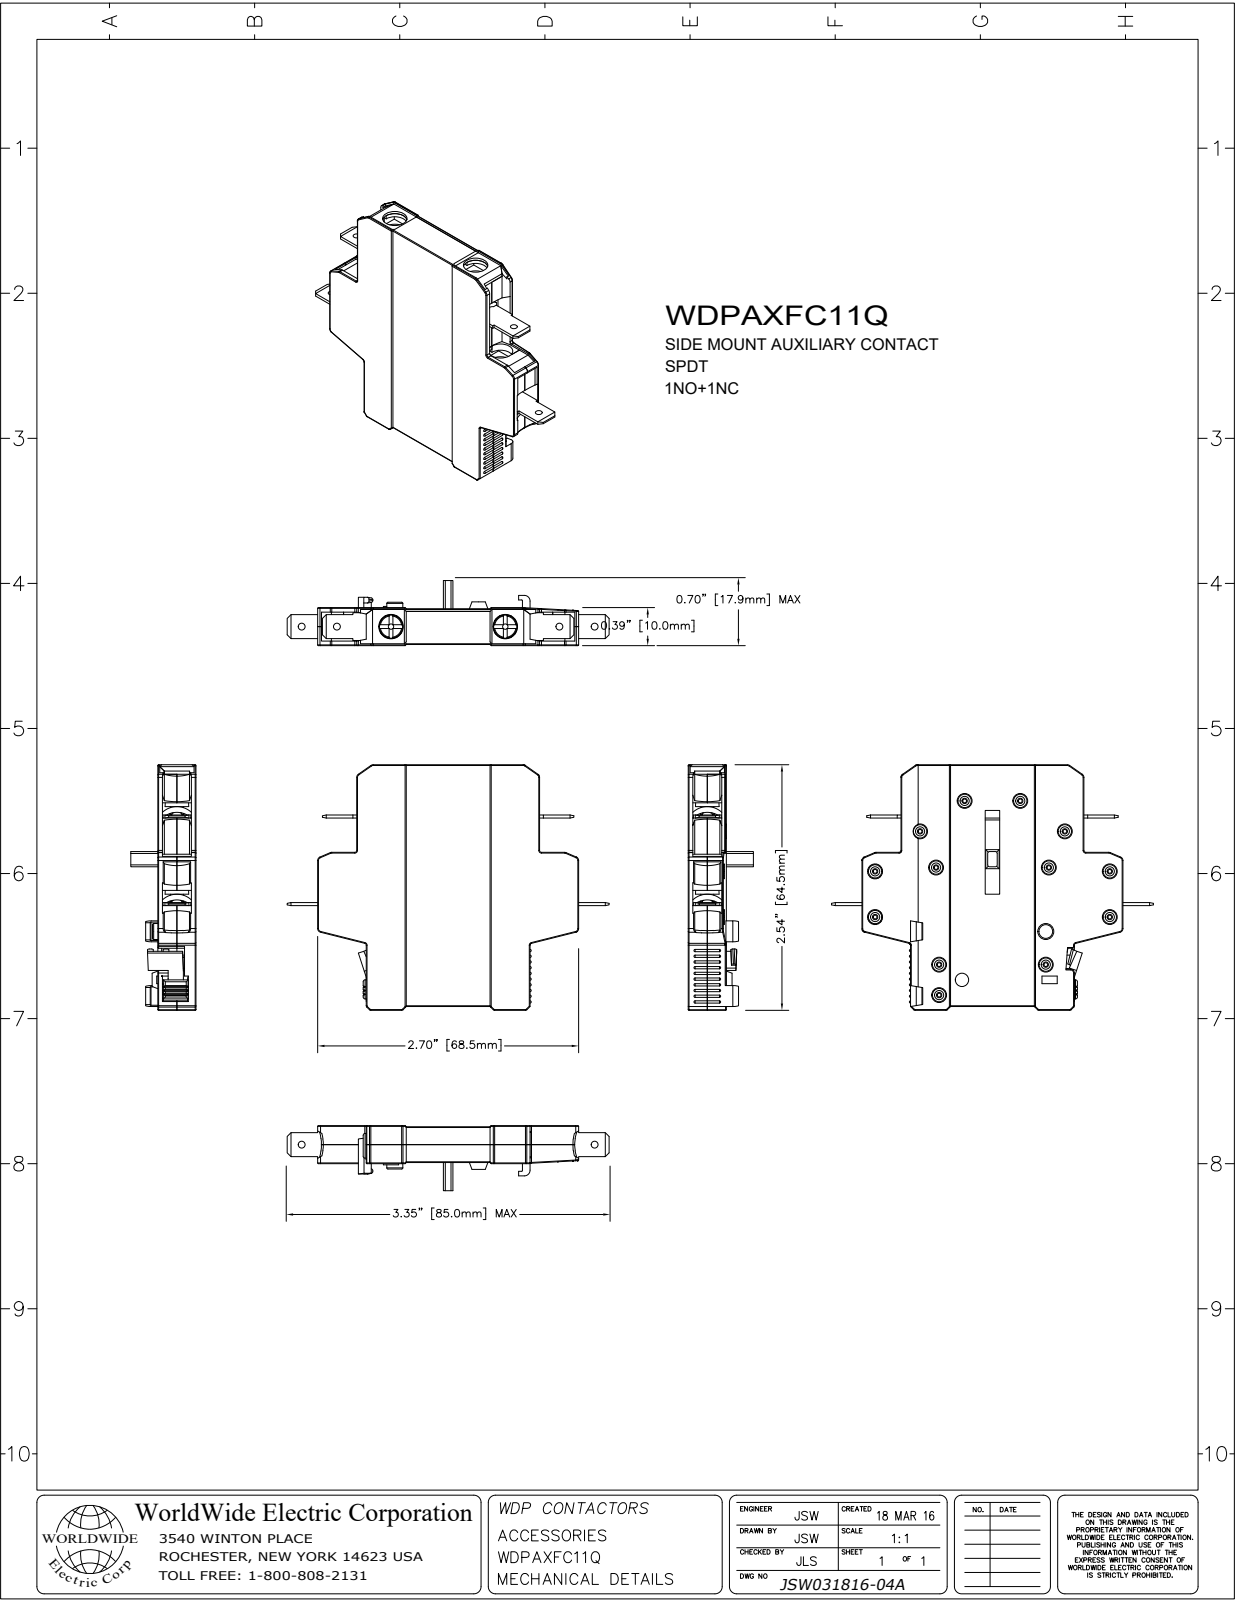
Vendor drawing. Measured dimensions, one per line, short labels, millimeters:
name: WDPAXFC11Q
written by: SolidWorks 2017 (AUTOMOTIVE_DESIGN)
unit: mm
bodies: 3 solids, 1015 faces (795 planar, 190 cylindrical, 30 other)
size: 70.2 × 66.8 × 22.2
volume: 17 190 mm³; area: 18 230 mm²
holes: 4× ⌀1.5, 4× ⌀3.1
bosses: 4× ⌀6, 4× ⌀2.5
rounds: 108× R0.3, 12× R3, 5× R1.5, 4× R0.5, 4× R0.8, 2× R0.8, 2× R1, 2× R1.1
face distances: 1.2, 10.2, 10.1, 1.5, 1.3, 11.4, 2, 8.2, 33.5, 0.8
hole spacings: 24.5, 41.4, 29.4, 38
